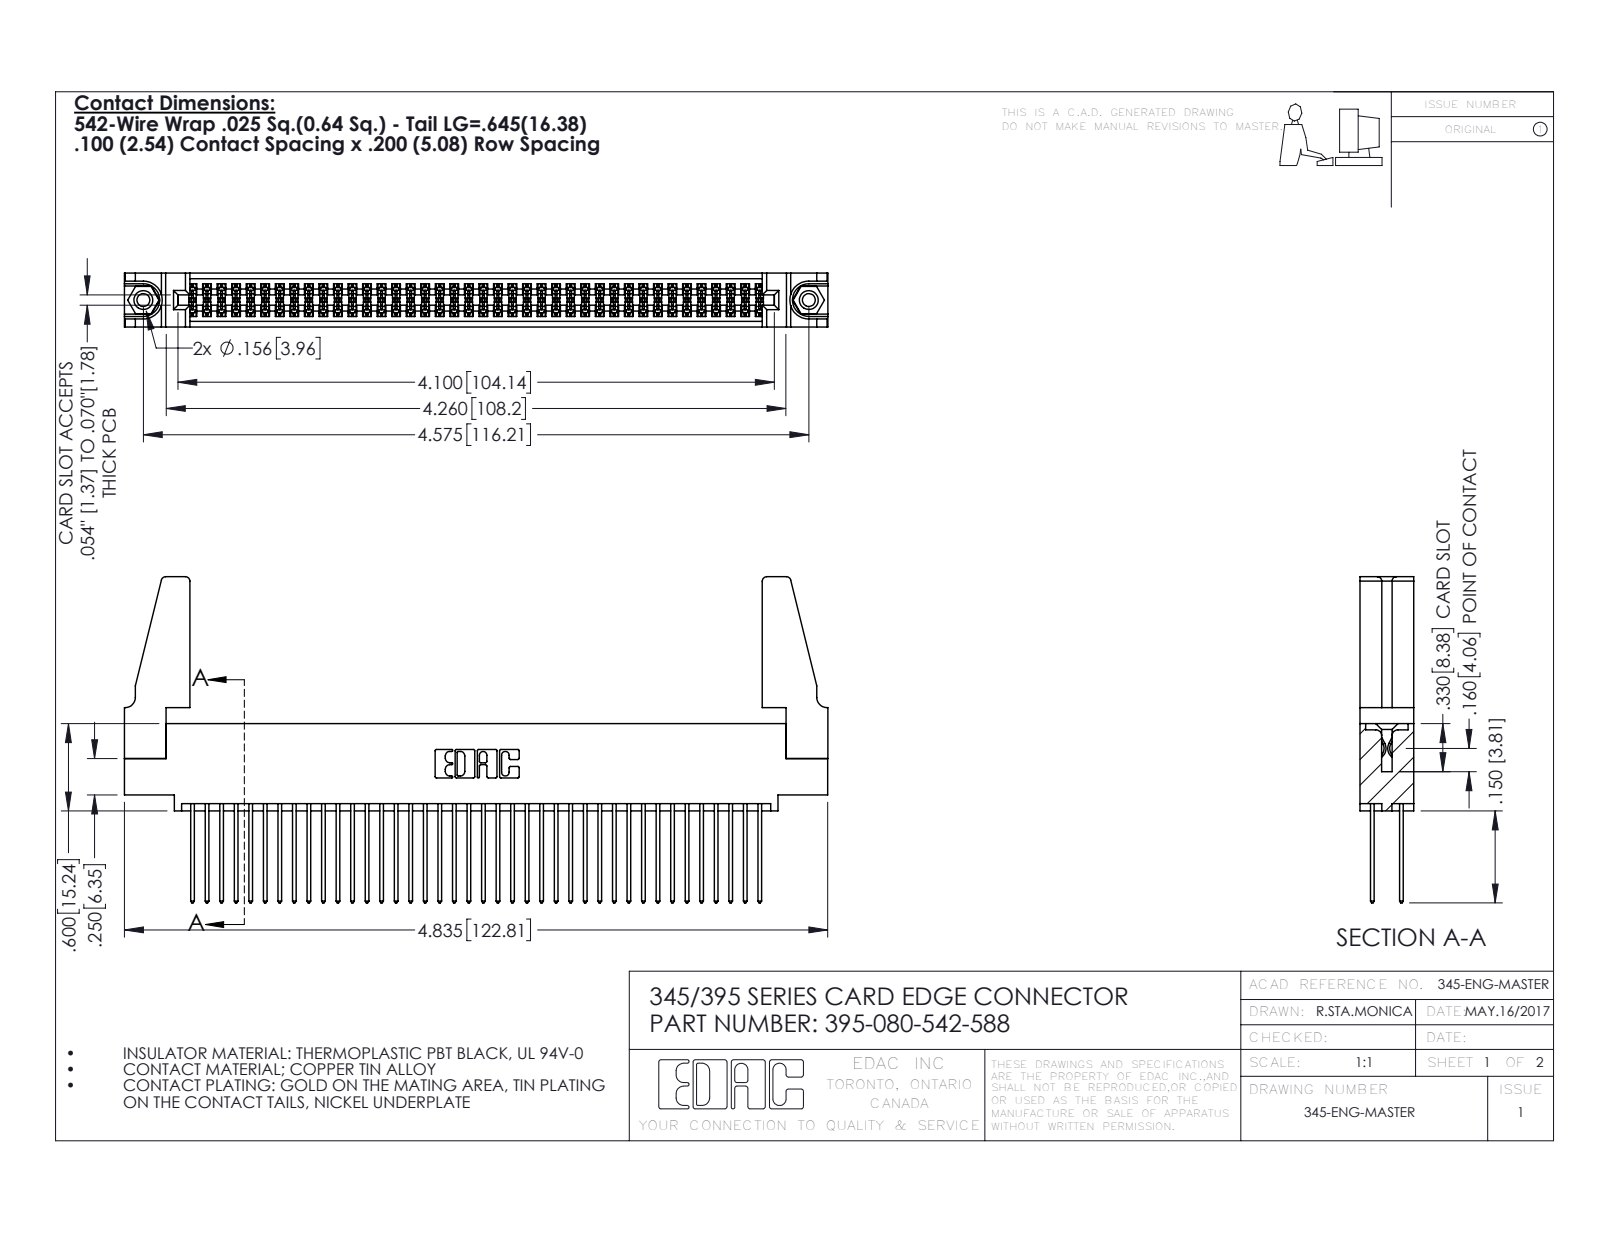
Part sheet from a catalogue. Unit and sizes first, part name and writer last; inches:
Units: inches
Overall size (bounding box): 4.836 × 2.242 × 0.37
Round holes (diameter × count): ⌀0.089 ×2, ⌀0.125 ×2, ⌀0.156 ×2, ⌀0.064 ×1
Round bosses / shafts (diameter × count): ⌀0.155 ×2
Partial cylindrical surfaces — rounded edges, fillets, slot ends (radius × count): R0.006 ×120, R0.01 ×80, R0.01 ×22, R0.03 ×8, R0.007 ×6, R0.031 ×6, R0.026 ×3, R0.014 ×2
Main face-to-face distances: 0.072, 0.298, 0.2, 0.098, 0.272, 0.025, 0.37, 0.225, 0.175, 0.149
Hole centre spacings: 0.27, 4.339, 4.575
Volume: 0.944 in³ · Surface area: 35.61 in²
Bodies: 85 solids, 4254 faces (2796 planar, 1442 cylindrical, 16 other)
Part name (STEP PRODUCT): 345-220-078_345-220-088; 345 Part_0.110 Offset - 0.156 Dia-TH; 345-292-001_345-293-142; 345-250-001_345-250-001-102 (+1 more)
STEP written by: SolidWorks 2016 (CONFIG_CONTROL_DESIGN)
